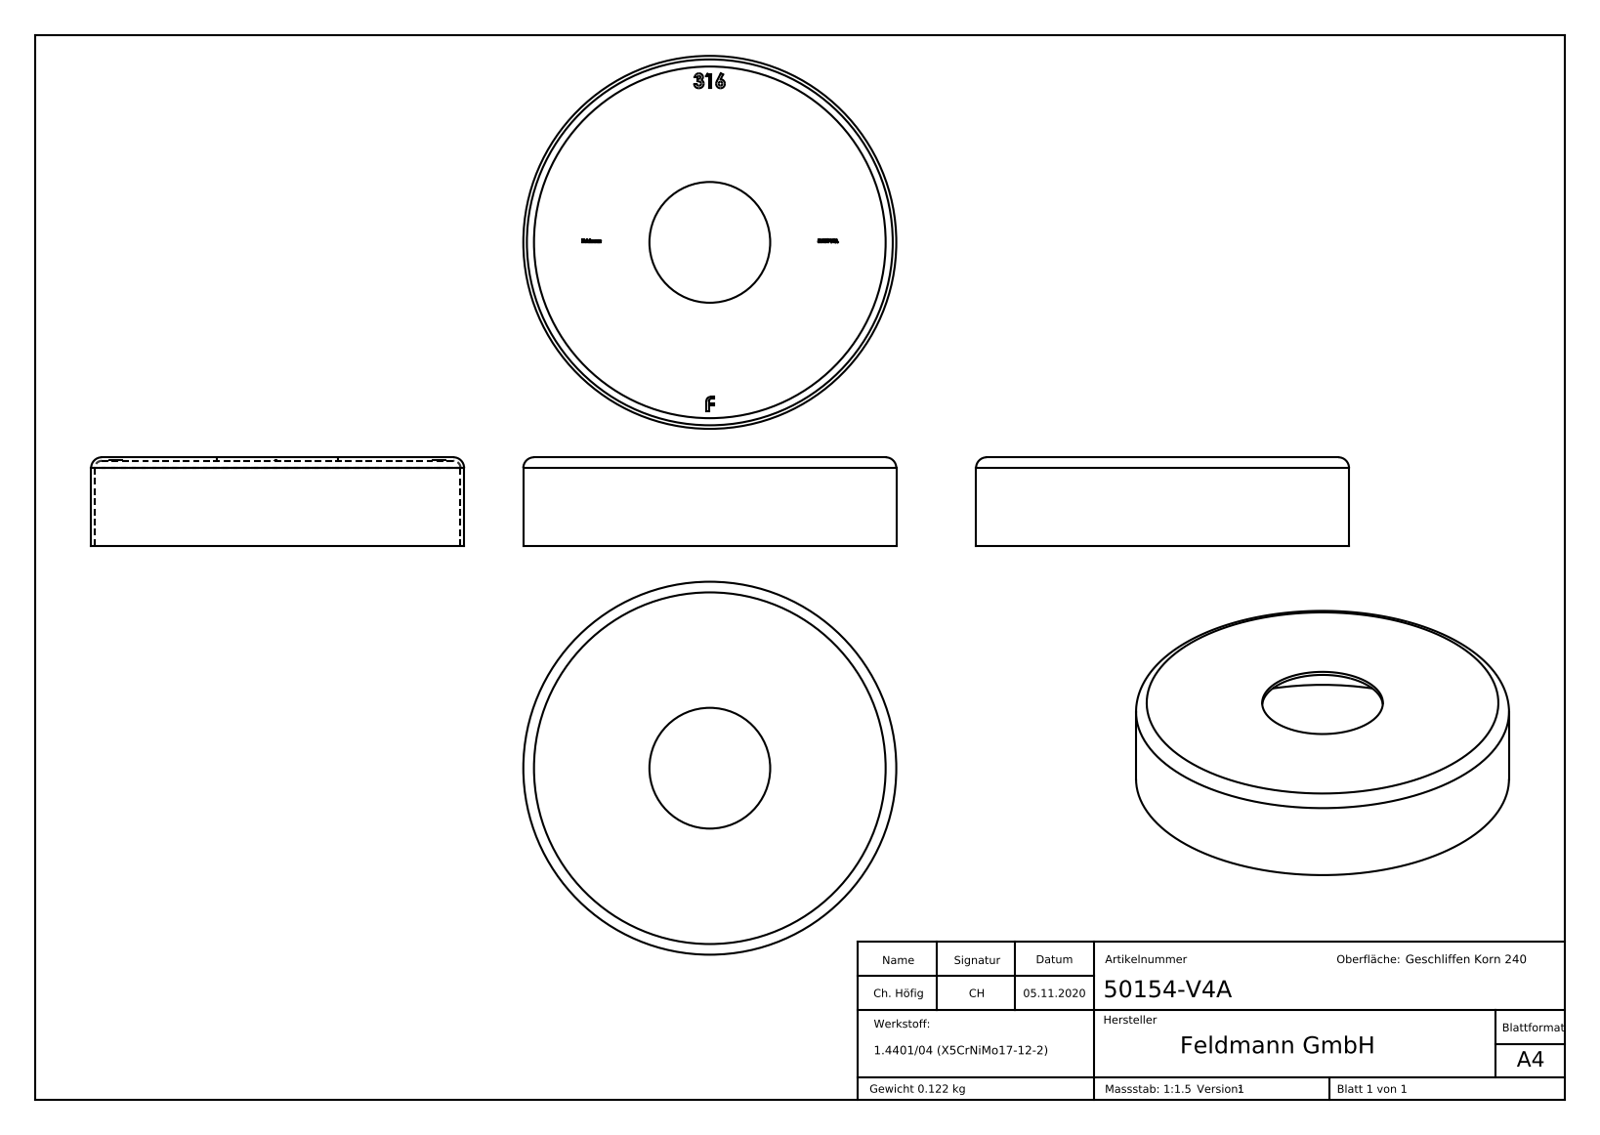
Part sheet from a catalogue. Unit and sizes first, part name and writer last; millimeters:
Units: millimetres
Overall size (bounding box): 105 × 105 × 25
Round holes (diameter × count): ⌀34 ×1, ⌀103 ×1
Round bosses / shafts (diameter × count): ⌀105 ×1
Main face-to-face distances: 1, 24, 25, 24.1, 0.9, 0.71, 1.44, 0.73, 46.02, 0.58
Volume: 15 237 mm³ · Surface area: 30 925 mm²
Bodies: 1 solid, 280 faces (174 planar, 6 cylindrical, 100 other)
Part name (STEP PRODUCT): 50154-V4A
STEP written by: SolidWorks 2018 (CONFIG_CONTROL_DESIGN)
